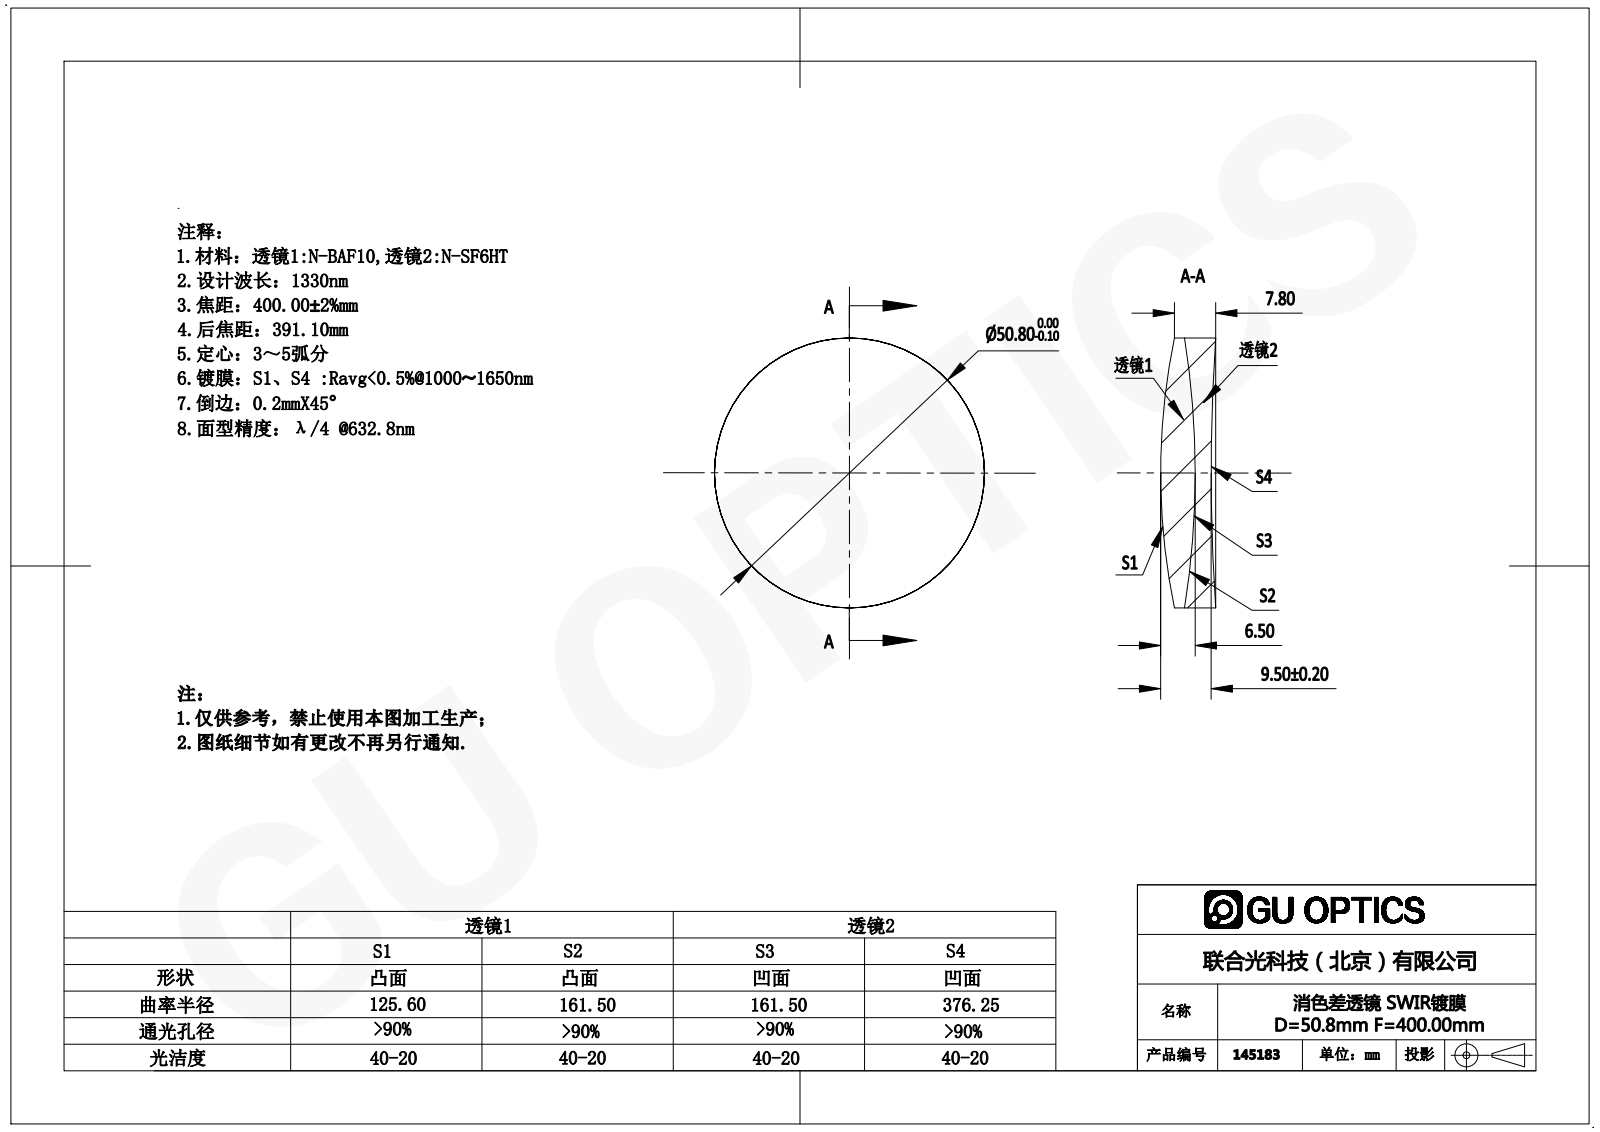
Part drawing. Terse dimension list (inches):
name: 145183
written by: SolidWorks 2016 (AUTOMOTIVE_DESIGN)
unit: in
bodies: 2 solids, 12 faces (0 planar, 4 cylindrical, 8 other)
size: 2 × 2 × 0.408
volume: 1.068 in³; area: 14.56 in²
bosses: 1× ⌀2
